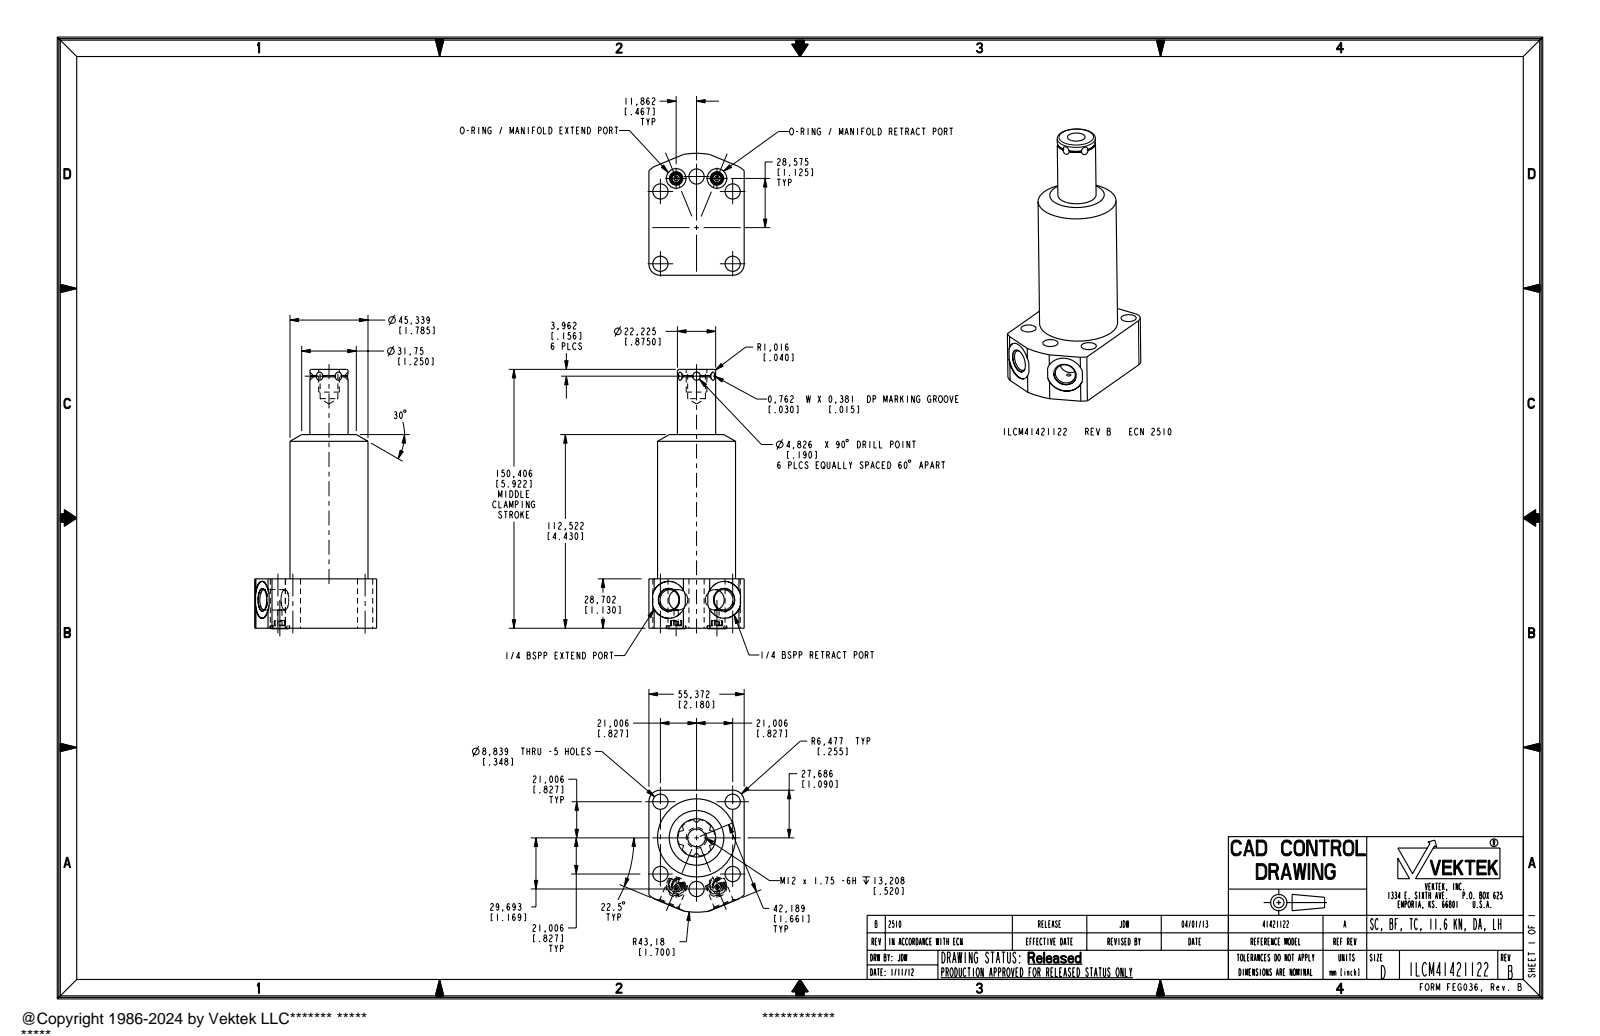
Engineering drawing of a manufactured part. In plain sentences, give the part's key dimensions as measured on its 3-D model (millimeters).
The part is named "ILCM41421122". Its 3-D file was written by "PRO/ENGINEER BY PARAMETRIC TECHNOLOGY CORPORATION, 2007460 (AUTOMOTIVE_DESIGN_CC2)". It is 1 solid with 141 faces: 52 planar, 59 cylindrical and 30 other. Overall it measures 150.71 by 70.87 by 55.37 millimeters. Its volume is 240 611 cubic millimeters and its surface area 34 509 square millimeters. Round holes: 5 of diameter 8.84, 2 of diameter 2.49, 2 of diameter 6.5, 2 of diameter 11.4, 2 of diameter 11.89, 2 of diameter 13.31, 2 of diameter 21.5, 1 of diameter 10.31. Round bosses or shafts: 2 of diameter 5.49, 1 of diameter 45.34, 1 of diameter 22.23, 1 of diameter 11.99. Partial cylindrical surfaces (rounded edges, fillets, slot ends): 2 of radius 6.48, 1 of radius 10.73, 1 of radius 43.18. The main face-to-face distances are 28.7, 55.38, 112.52, 83.82, 150.4, 121.7, 37.88, 14.43, 14.17, 1.45. The hole center spacings are 29.71, 42.02, 11.87, 11.91, 22.73, 30.93, 33.73, 50.42.
